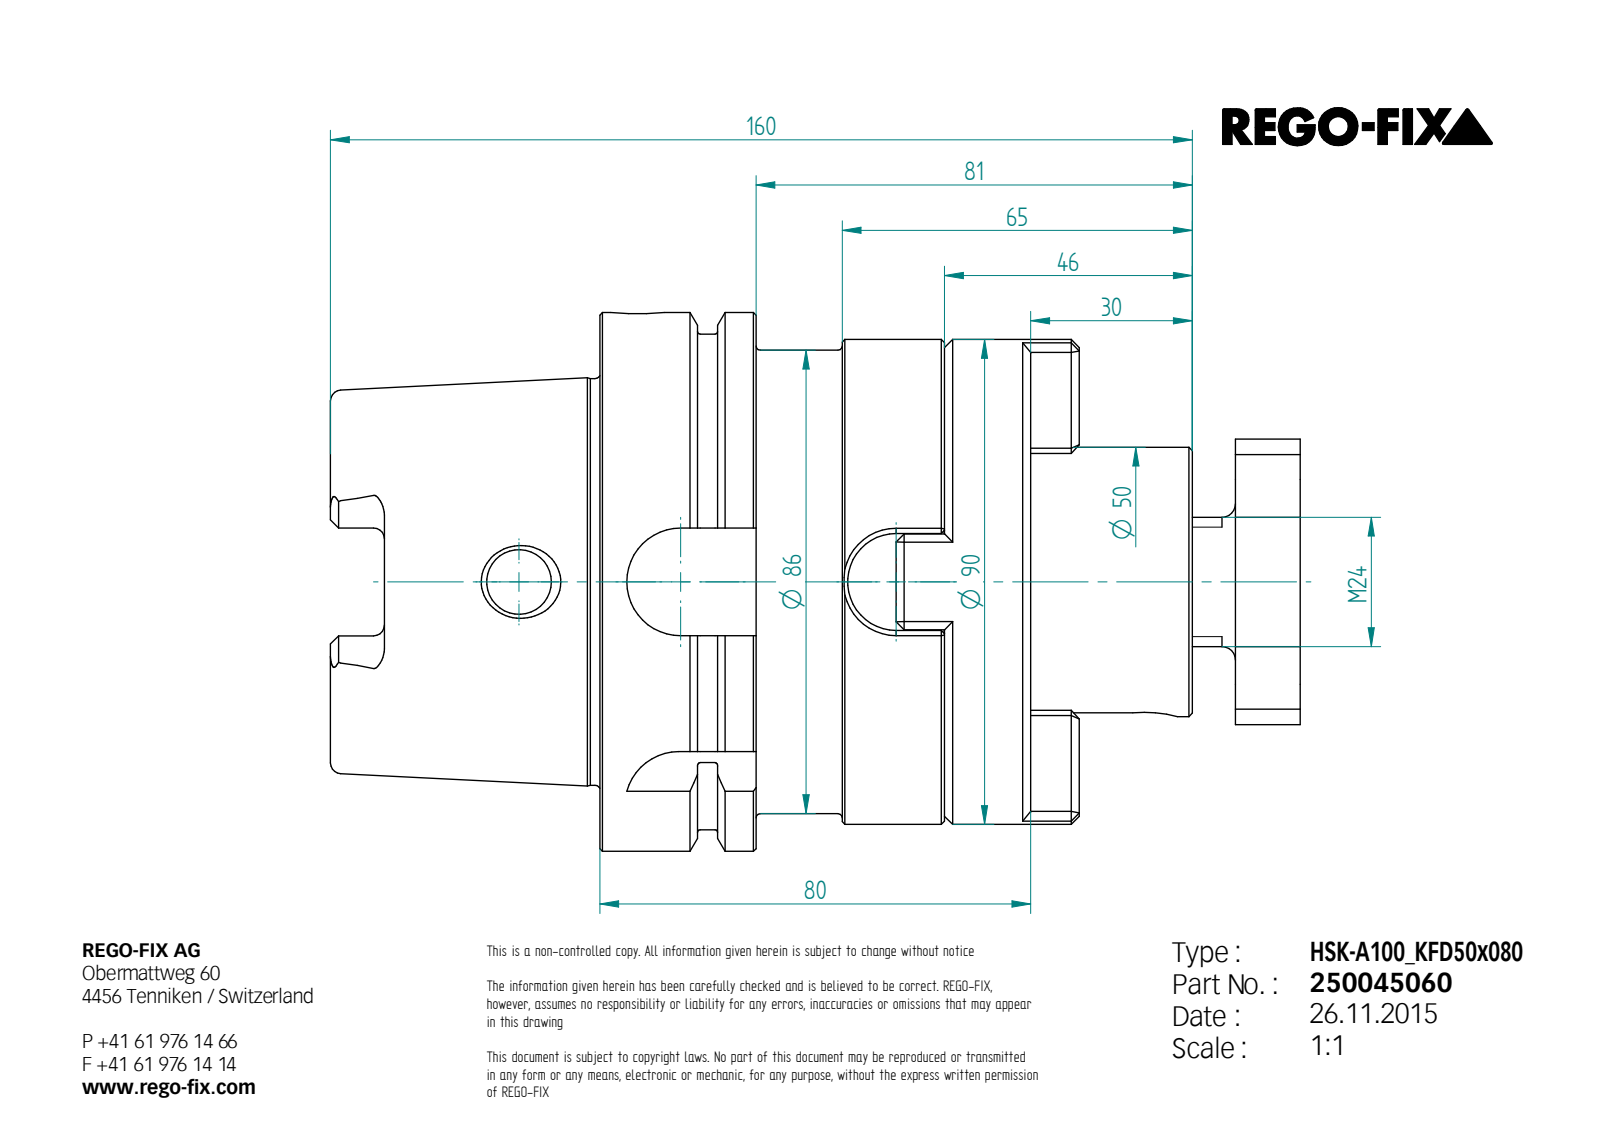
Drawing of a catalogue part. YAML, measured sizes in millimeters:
step_written_by: "Unknown (AUTOMOTIVE_DESIGN)"
units: millimeters
bodies: {solids: 3, faces: 260, planar: 126, cylindrical: 54, other: 80}
overall_size: [180, 100, 100]
volume: 641708
surface_area: 99115
round_holes:
  - {diameter: 12, count: 2}
  - {diameter: 8.5, count: 1}
  - {diameter: 10, count: 1}
  - {diameter: 20.75, count: 1}
  - {diameter: 22.38, count: 1}
  - {diameter: 25, count: 1}
  - {diameter: 50, count: 1}
  - {diameter: 63, count: 1}
round_bosses_or_shafts:
  - {diameter: 100, count: 1}
  - {diameter: 92, count: 1}
  - {diameter: 90, count: 1}
  - {diameter: 86, count: 1}
  - {diameter: 75.46, count: 1}
  - {diameter: 53, count: 1}
  - {diameter: 49.4, count: 1}
  - {diameter: 24, count: 1}
partial_cylinders:
  - {radius: 2, count: 6}
  - {radius: 4.88, count: 4}
  - {radius: 7, count: 4}
  - {radius: 6, count: 2}
  - {radius: 10, count: 2}
  - {radius: 9, count: 1}
  - {radius: 11, count: 1}
face_to_face_distances: [16, 64, 80, 50, 130, 29, 66, 51.5, 35, 89]
